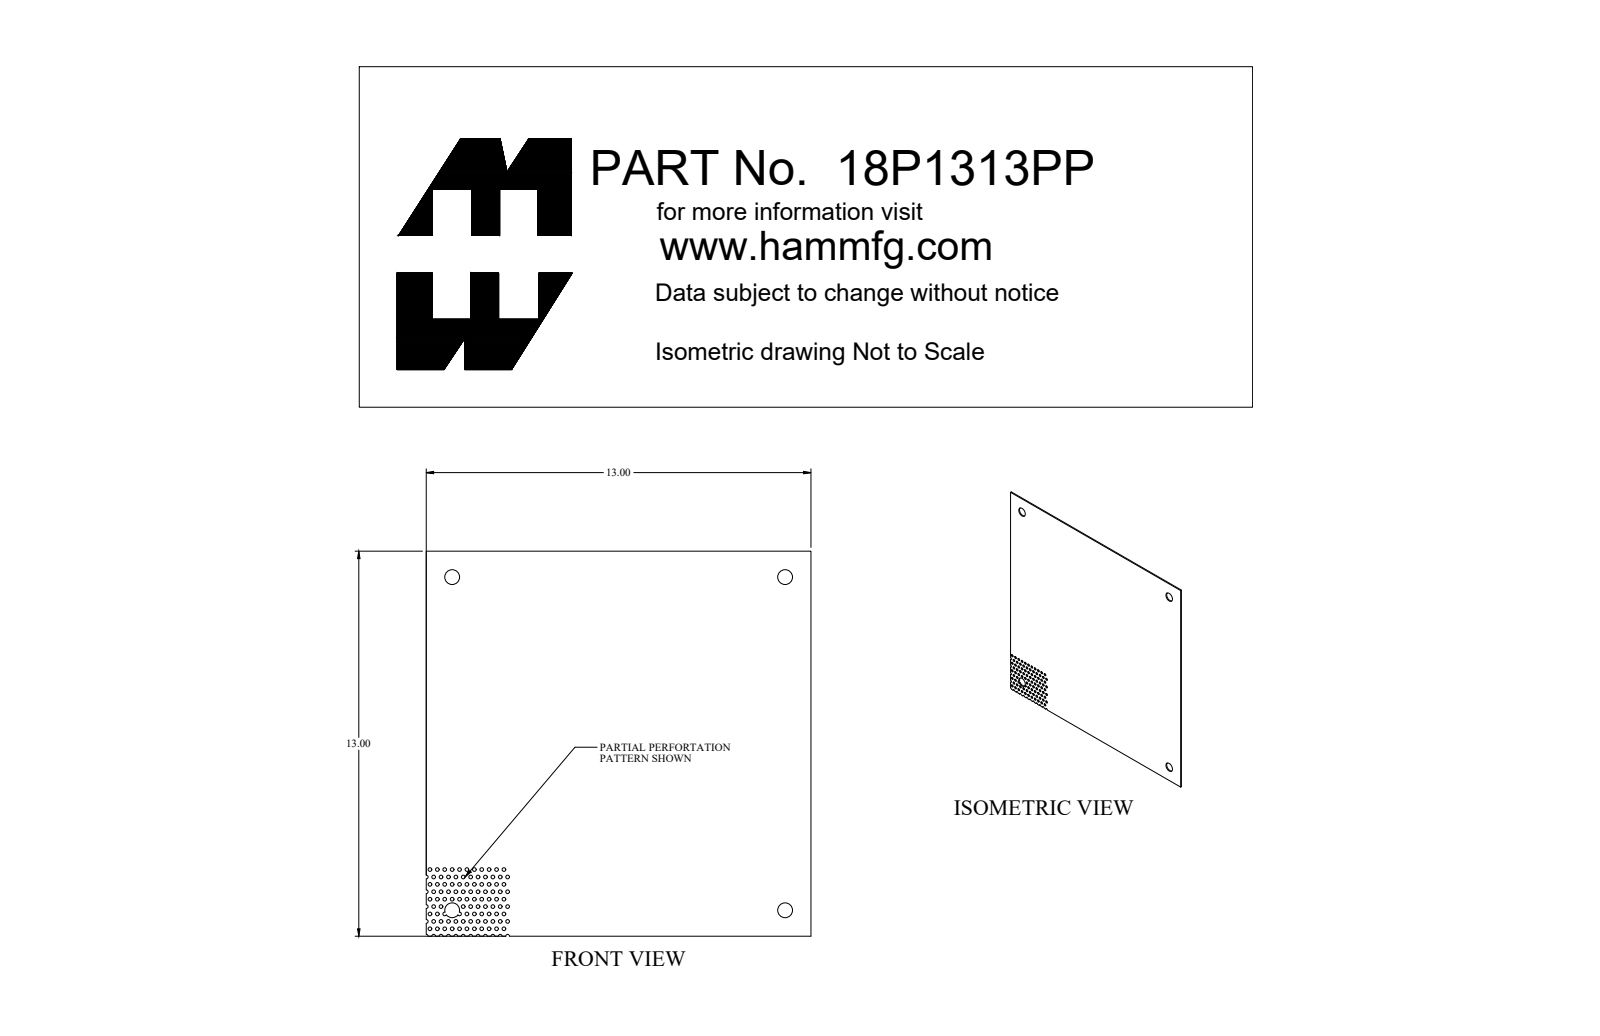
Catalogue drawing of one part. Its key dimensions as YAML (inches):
part_name: "18P1313PP_Default"
step_written_by: "SolidWorks 2018 (CONFIG_CONTROL_DESIGN)"
units: inches
bodies: {solids: 1, faces: 251, planar: 21, cylindrical: 230, other: 0}
overall_size: [13, 13, 0.057]
volume: 9.516
surface_area: 339.4
round_holes:
  - {diameter: 0.125, count: 61}
  - {diameter: 0.125, count: 33}
  - {diameter: 0.5, count: 4}
partial_cylinders:
  - {radius: 0.062, count: 17}
  - {radius: 0.063, count: 1}
face_to_face_distances: [0.057, 13]
hole_center_spacings: [0.28, 0.25, 0.5, 0.45, 0.451, 0.673, 0.673, 0.91]
